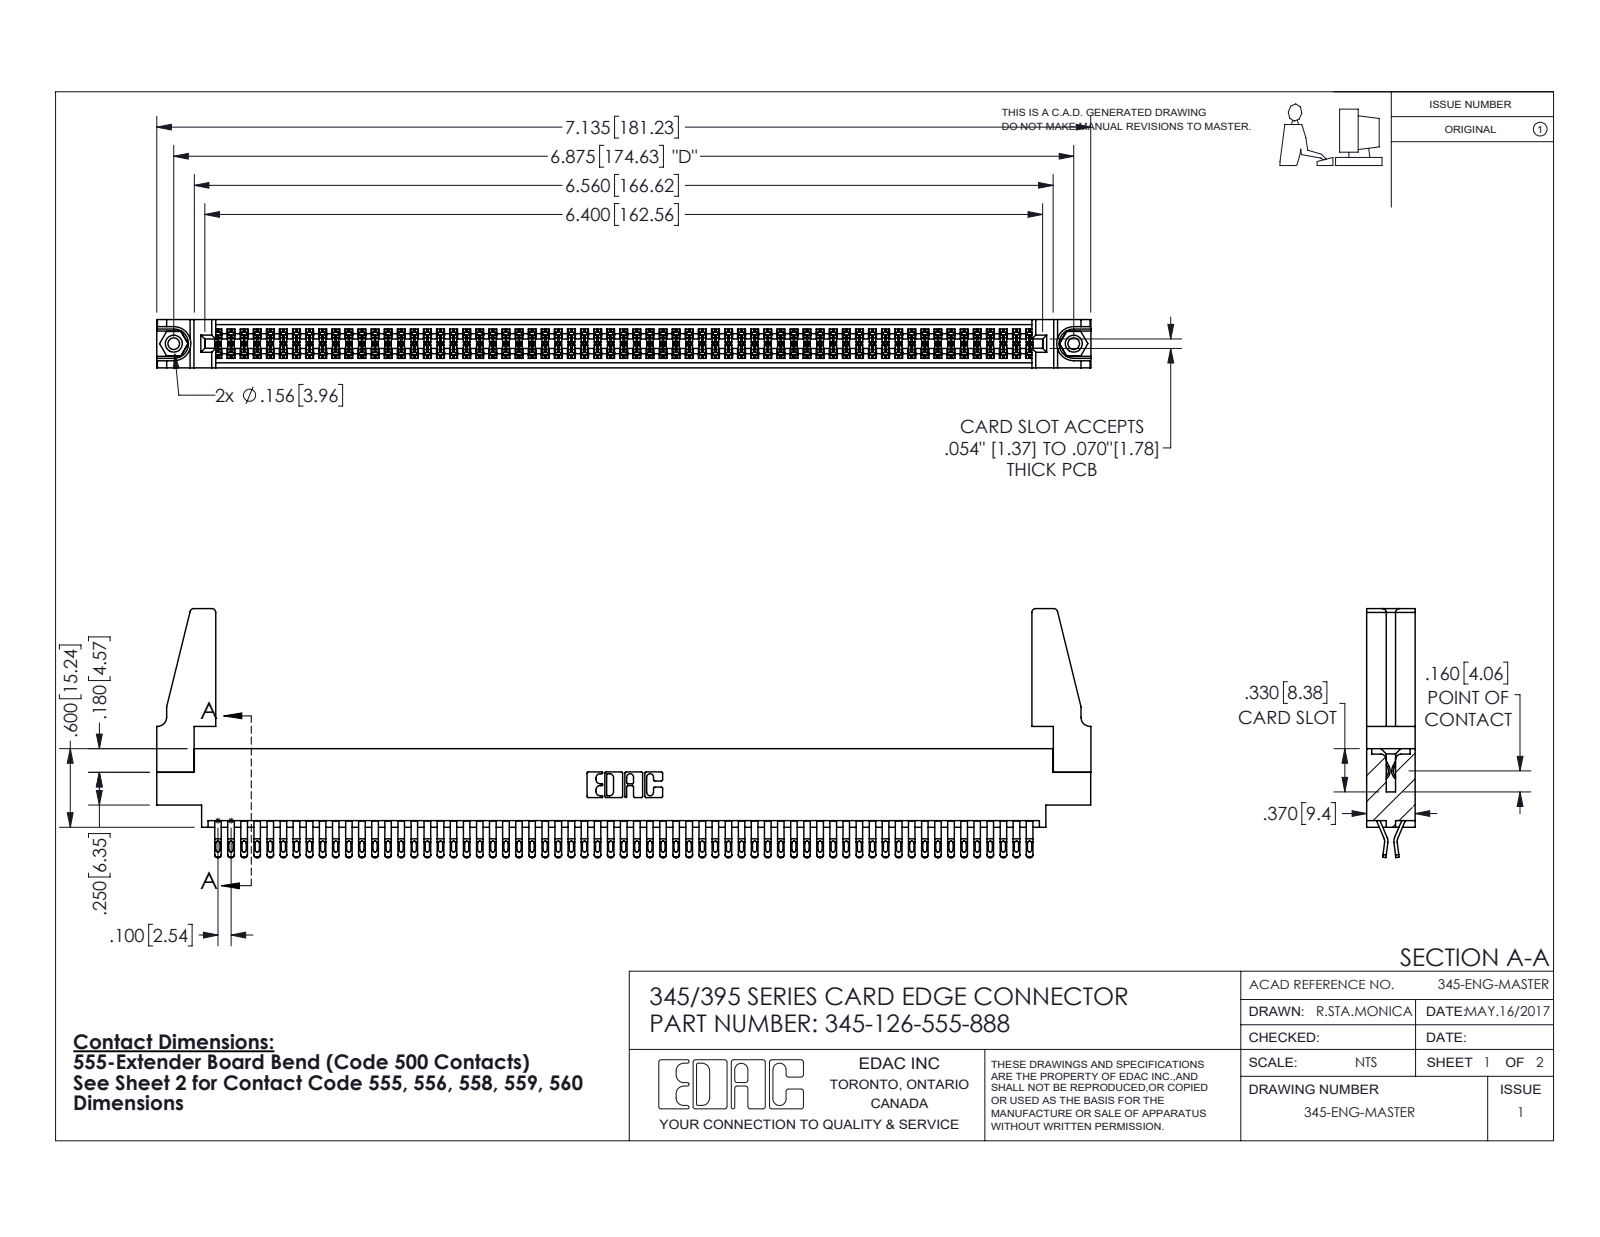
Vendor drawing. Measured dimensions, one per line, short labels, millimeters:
name: 345-126-555-888; 345-220-078_345-220-088; 345-250-001_345-250-001-102; 345-292-001_555 Tail (+1 more)
written by: SolidWorks 2016 (CONFIG_CONTROL_DESIGN)
unit: mm
bodies: 131 solids, 7310 faces (4062 planar, 3232 cylindrical, 16 other)
size: 181.3 × 48.3 × 9.4
volume: 21 300 mm³; area: 31 630 mm²
holes: 2× ⌀2.3, 2× ⌀3.2, 2× ⌀4, 1× ⌀1.6
bosses: 2× ⌀3.9
rounds: 315× R0.4, 252× R0.5, 189× R0.2, 22× R0.3, 8× R0.8, 6× R0.2, 6× R0.8, 3× R0.7
face distances: 1.8, 7.6, 9.4, 0.6, 5.1, 2.5, 6.9, 5.7, 4.4, 3.8
hole spacings: 6.9, 168.6, 174.6
